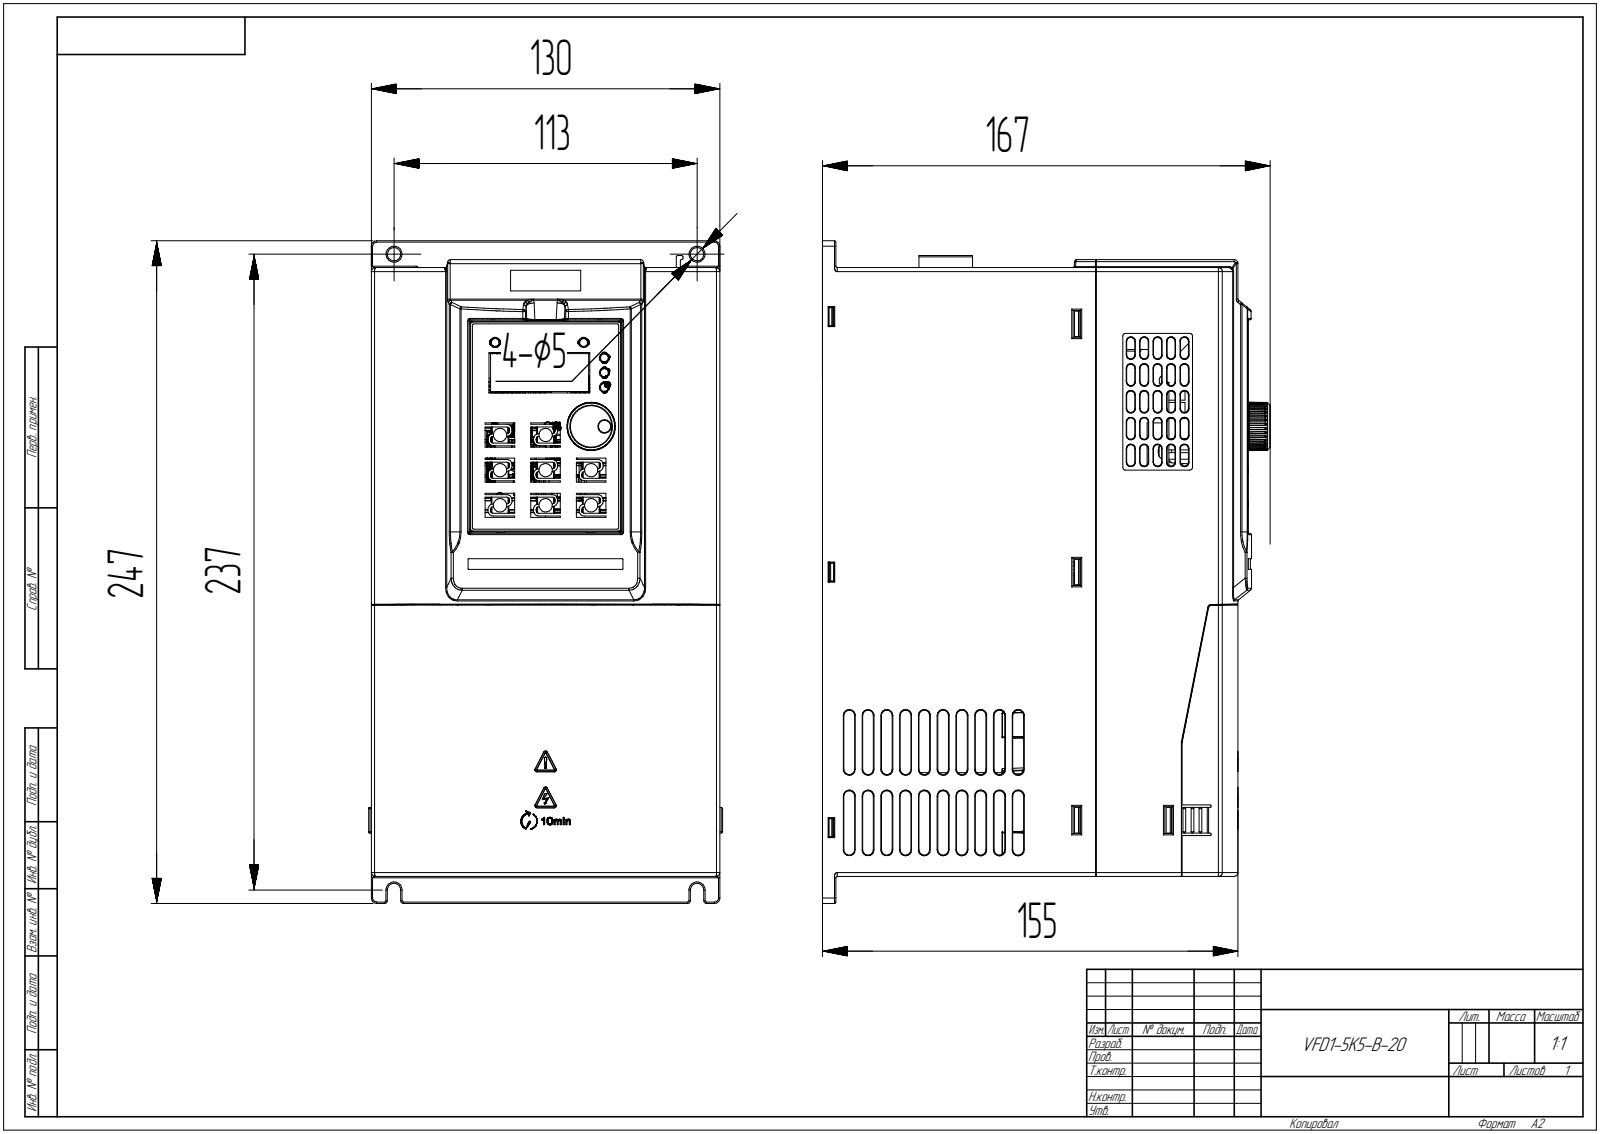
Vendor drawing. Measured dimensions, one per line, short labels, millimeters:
name: PRT0002
written by: CREO PARAMETRIC BY PTC INC, 2020074 (CONFIG_CONTROL_DESIGN)
unit: mm
bodies: 1 solid, 8171 faces (4631 planar, 1851 cylindrical, 1689 other)
size: 247 × 167 × 132
volume: 4 167 000 mm³; area: 672 210 mm²
holes: 15× ⌀1.5, 12× ⌀1.8, 7× ⌀2.5, 7× ⌀3.8, 6× ⌀1.2, 4× ⌀2, 4× ⌀3.5, 3× ⌀4.5, 3× ⌀9.5, 2× ⌀1, 2× ⌀5, 1× ⌀2.7
bosses: 8× ⌀5, 8× ⌀3.5, 8× ⌀3, 6× ⌀4, 4× ⌀6, 4× ⌀5.5, 4× ⌀5.4, 3× ⌀11.5
rounds: 465× R0.5, 295× R0.2, 185× R1, 56× R2, 48× R0.3, 35× R0.34, 27× R2.7, 14× R1.5
face distances: 2.2, 1.23, 128.77, 127.54, 1.5, 130, 4, 79.2, 1.8, 225.5
hole spacings: 235.1, 9.75, 10.1, 19.85, 41.4, 50.56, 51.15, 61.25
